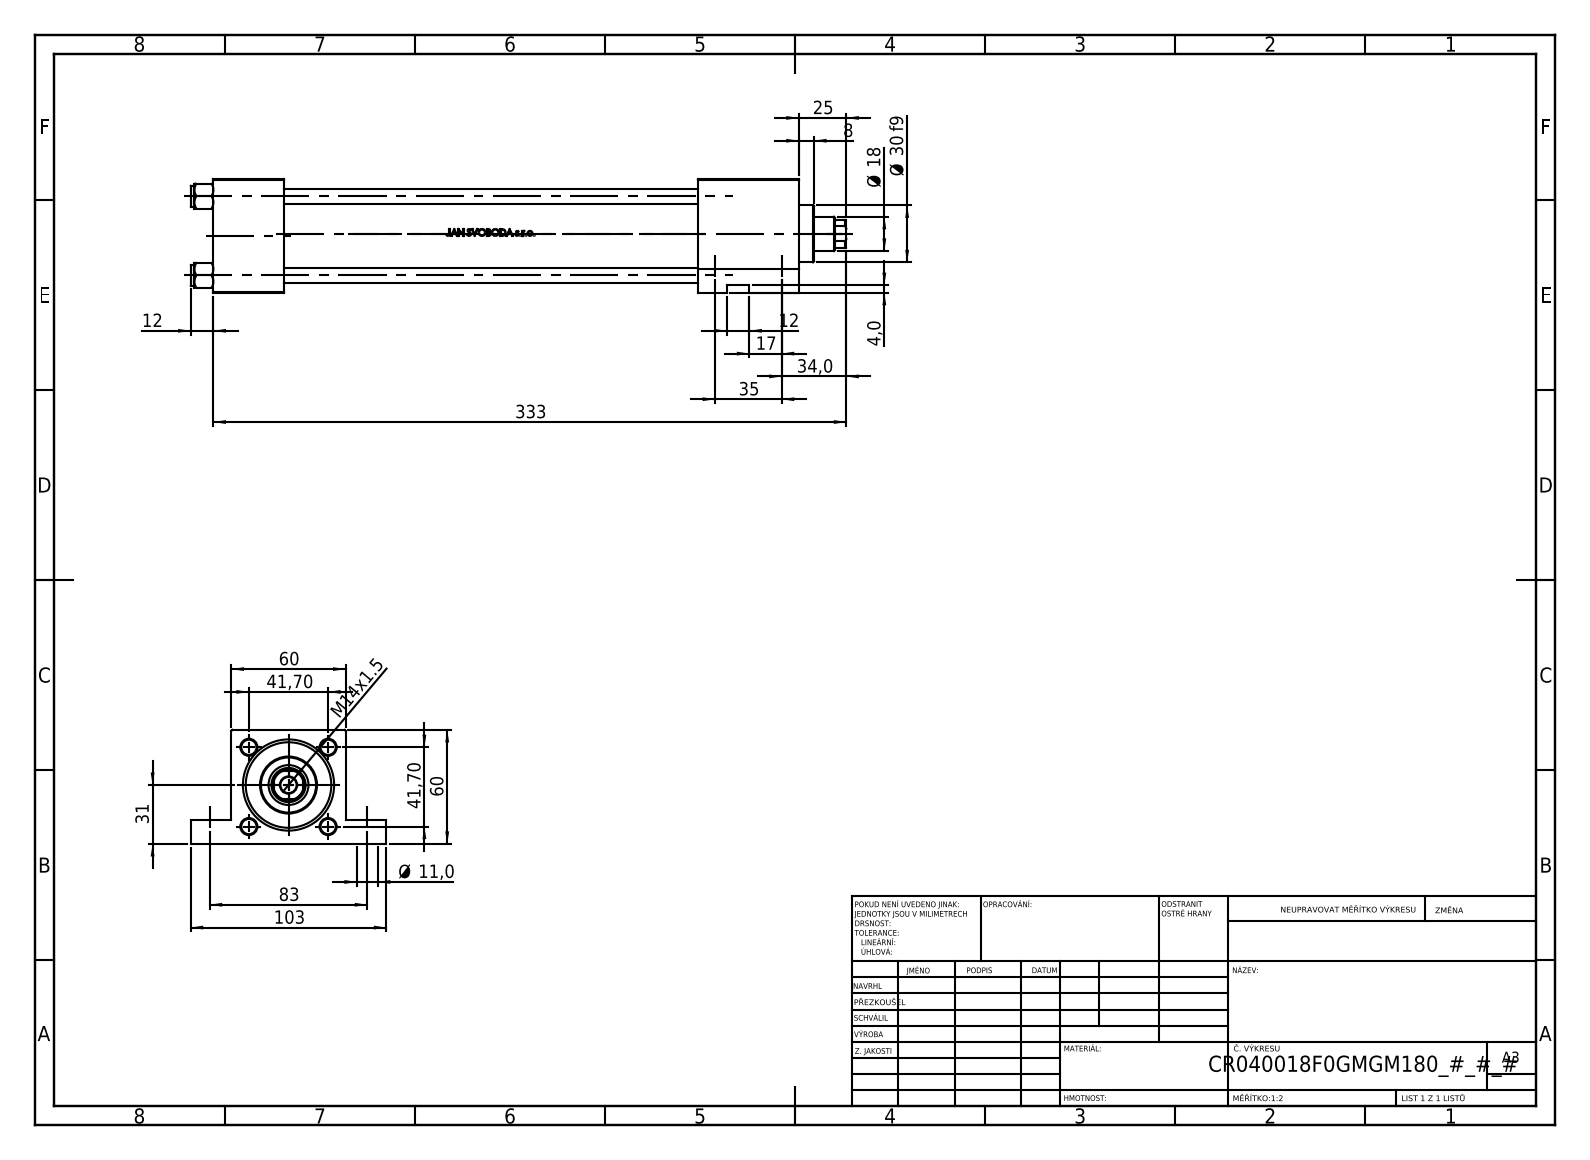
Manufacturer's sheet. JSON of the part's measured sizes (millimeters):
{"part_name": "V215_VC_A; V215CR_F_Body; NUT_M5_F; V215CR_VCP_F (+1 more)", "step_written_by": "SolidWorks 2019 (CONFIG_CONTROL_DESIGN)", "units": "millimeters", "bodies": {"solids": 11, "faces": 1118, "planar": 437, "cylindrical": 141, "other": 540}, "overall_size": [345, 103, 60], "volume_mm3": 560775, "surface_area_mm2": 180166, "round_holes": [[8, 4], [11, 4], [7, 2], [24, 2], [8.5, 1], [16, 1], [16.66, 1], [18, 1], [21, 1], [31, 1], [40, 1], [45, 1]], "round_bosses_or_shafts": [[11, 4], [46, 1], [30, 1]], "partial_cylinders_radius": [[8.5, 1]], "face_to_face_distances": [60, 37, 308, 271, 255, 218, 53, 279.3, 242.3, 24.3], "hole_center_spacings": [41.7, 28.79, 30.2, 35, 58.97, 83, 90.08, 252.5]}
